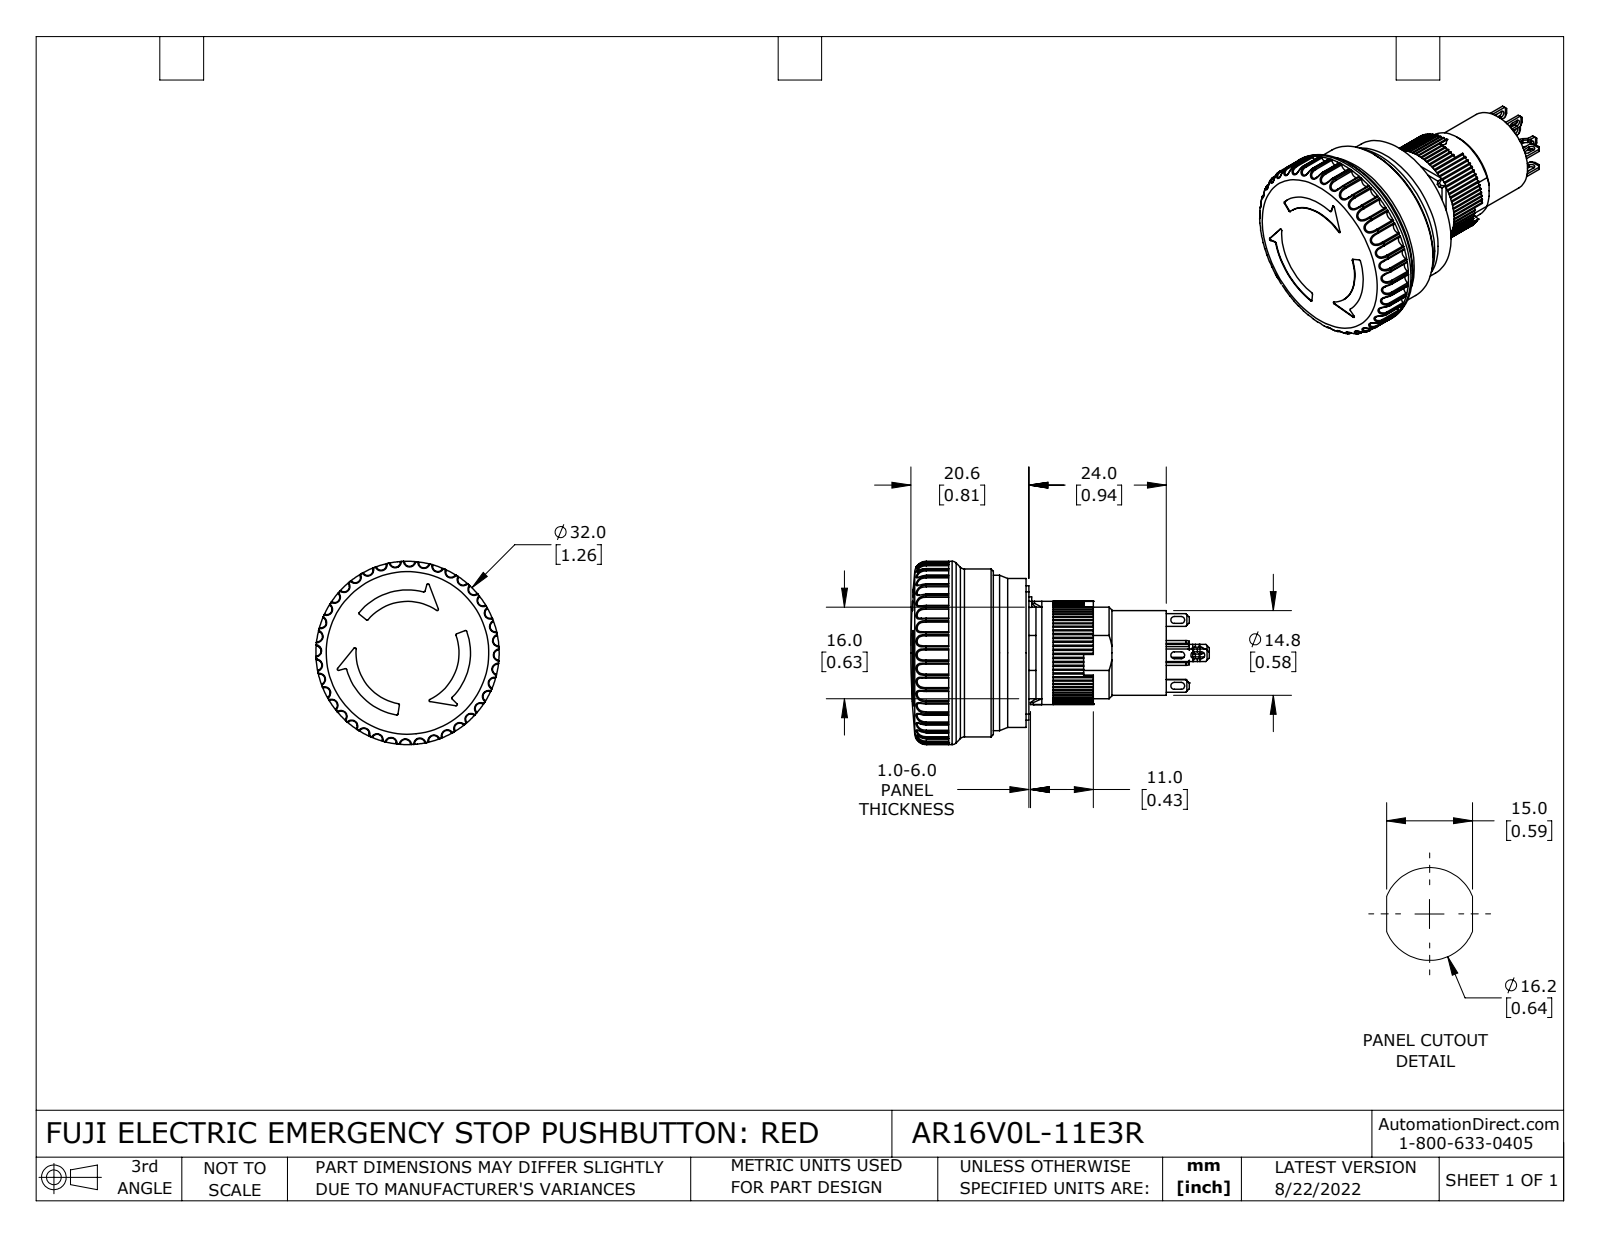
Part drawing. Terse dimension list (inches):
name: AR16V0L-11E3R
written by: SolidWorks 2021 (CONFIG_CONTROL_DESIGN)
unit: in
bodies: 7 solids, 1001 faces (540 planar, 387 cylindrical, 74 other)
size: 2.051 × 1.26 × 1.26
volume: 1.124 in³; area: 13.68 in²
holes: 1× ⌀0.583, 1× ⌀0.63, 1× ⌀1.069
bosses: 1× ⌀1.26, 1× ⌀1.154, 1× ⌀1.024, 1× ⌀0.858, 1× ⌀0.709, 1× ⌀0.236
rounds: 80× R0.008, 80× R0.01, 40× R0.035, 16× R0.024, 8× R0.02, 4× R0.01, 4× R0.029, 2× R0.039
face distances: 0.421, 0.53, 0.108, 0.039, 0.02, 0.069, 0.856, 0.49, 0.089, 0.049
